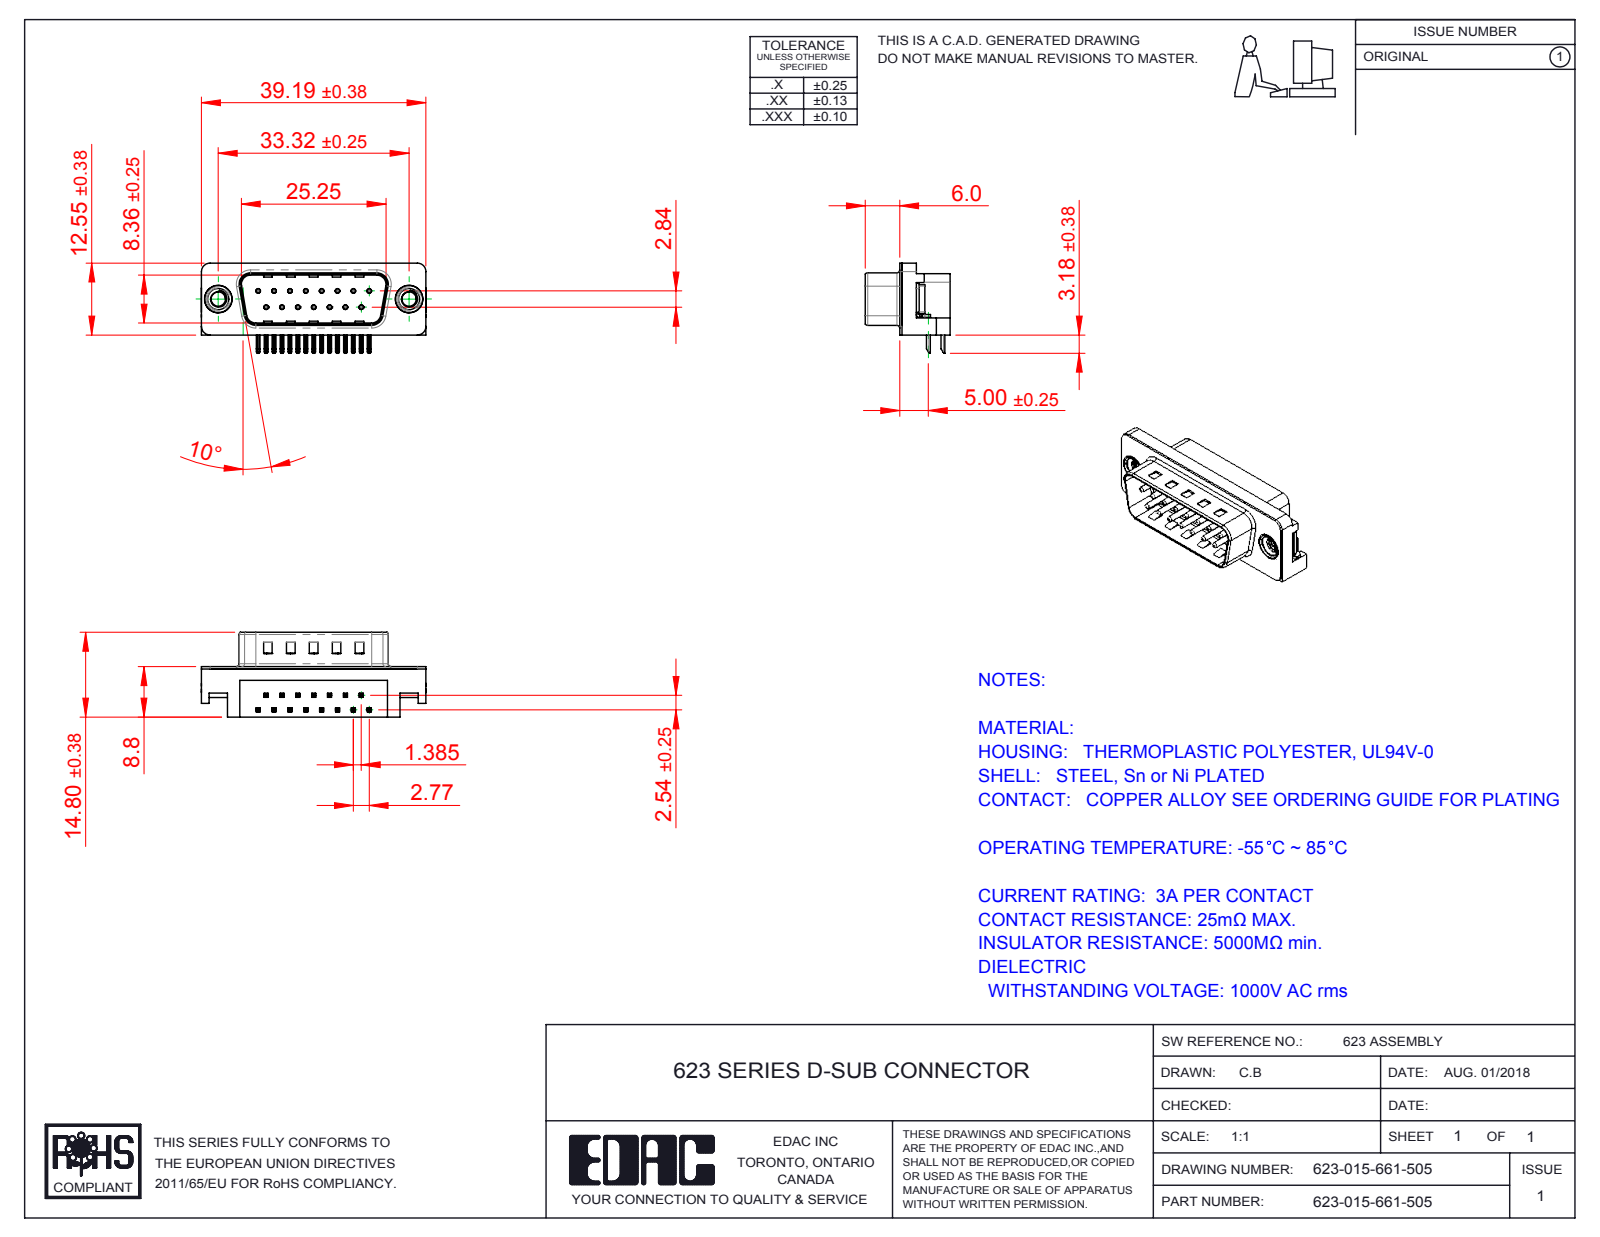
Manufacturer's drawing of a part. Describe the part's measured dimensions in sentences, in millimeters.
The part is named "623 Housing_15 Socket; 623 Shell_15 Socket; 623 Non Board Mount; 623 M3 Threaded Rivet (+3 more)". Its 3-D file was written by "SolidWorks 2016 (CONFIG_CONTROL_DESIGN)". It is 21 solids with 1467 faces: 893 planar, 439 cylindrical and 135 other. Overall it measures 39.22 by 15.73 by 14.8 millimeters. Its volume is 3 313 cubic millimeters and its surface area 4 888 square millimeters. Round holes: 15 of diameter 0.35, 15 of diameter 0.8, 2 of diameter 2.5, 2 of diameter 4, 2 of diameter 4.8, 2 of diameter 5. Round bosses or shafts: 15 of diameter 0.75, 2 of diameter 4.9, 2 of diameter 4.75, 2 of diameter 3.9. Partial cylindrical surfaces (rounded edges, fillets, slot ends): 68 of radius 0.25, 30 of radius 0.12, 16 of radius 1, 9 of radius 0.5, 6 of radius 1.5, 4 of radius 0.9, 4 of radius 1.6, 4 of radius 2. The main face-to-face distances are 0.4, 8.4, 2.1, 1.7, 10.46, 8.8, 10.86, 8.76, 5.9, 2.9. The hole center spacings are 3.16, 2.77, 5.54, 8.31, 11.08, 5.03, 5.04, 7.48.
